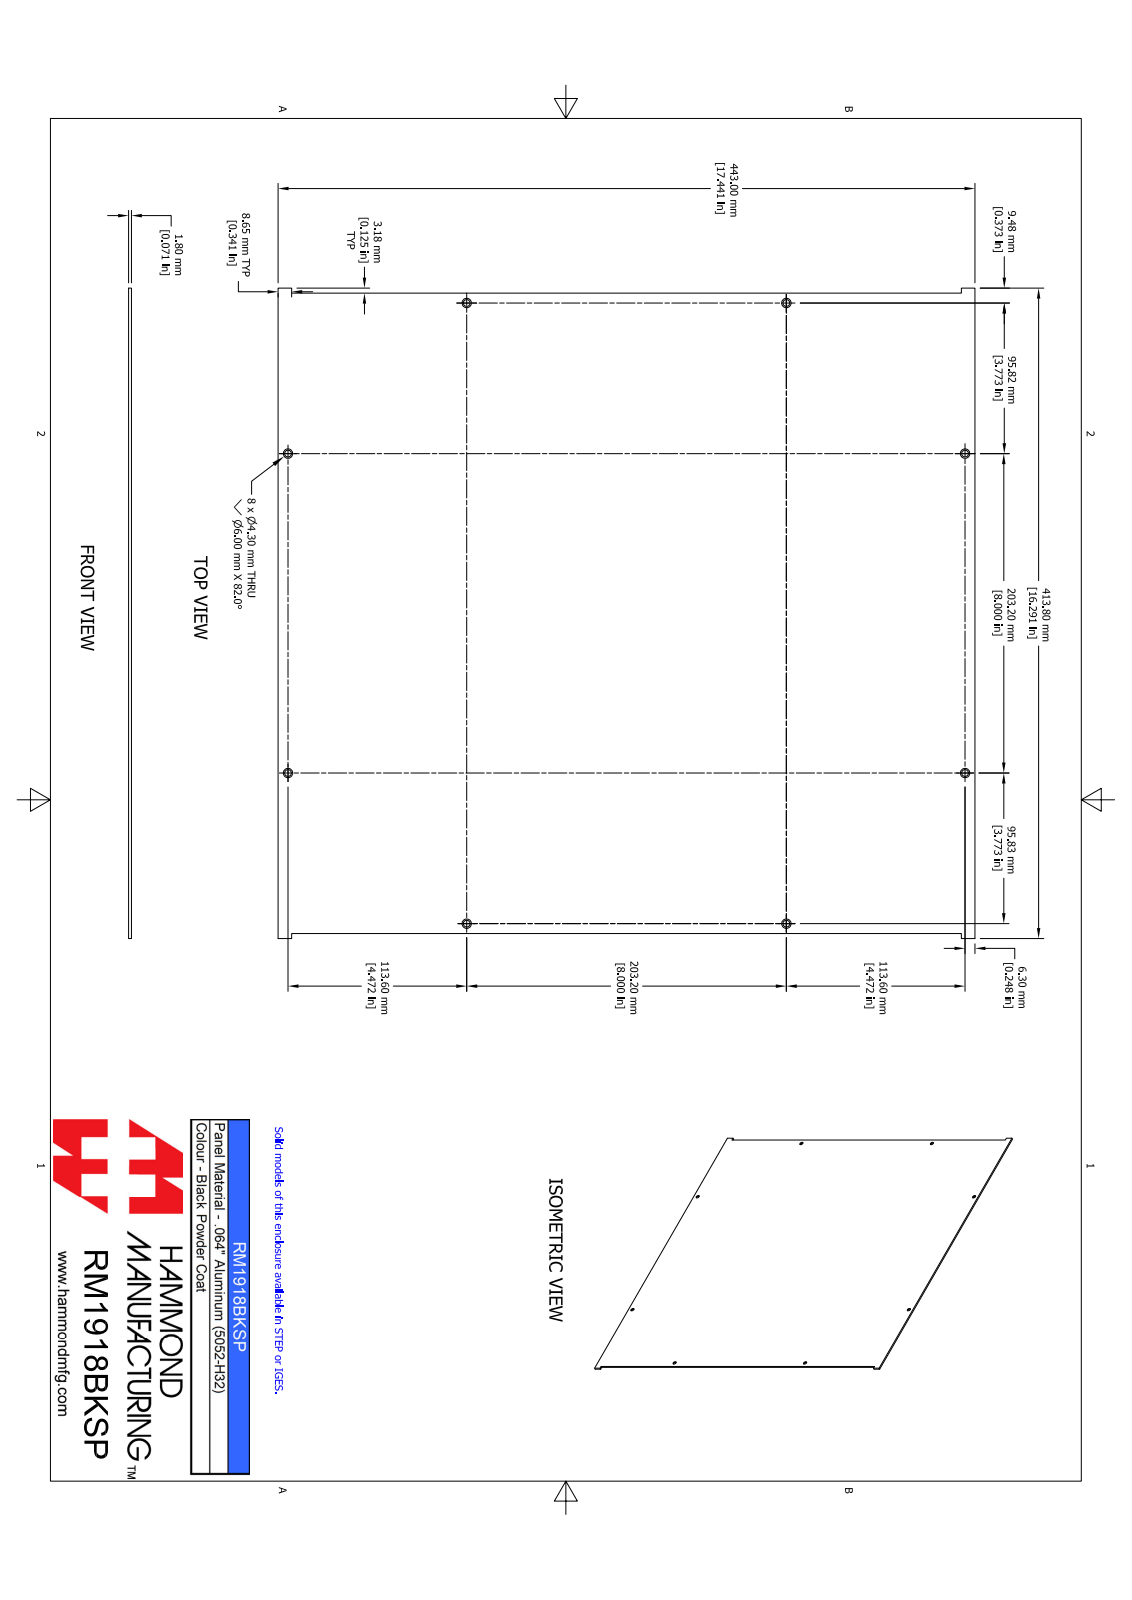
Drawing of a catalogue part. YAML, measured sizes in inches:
part_name: "RM1918BKSP"
step_written_by: "SolidWorks 2021 (AUTOMOTIVE_DESIGN)"
units: inches
bodies: {solids: 1, faces: 30, planar: 14, cylindrical: 8, other: 8}
overall_size: [17.441, 16.291, 0.071]
volume: 19.82
surface_area: 564.6
round_holes:
  - {diameter: 0.169, count: 8}
face_to_face_distances: [0.071, 16.041, 17.441, 0.125, 16.167, 16.291, 16.166, 0.125, 0.341, 17.1]
hole_center_spacings: [5.851, 8, 12.593, 12.594, 13.03, 13.031, 15.545, 16.945]
